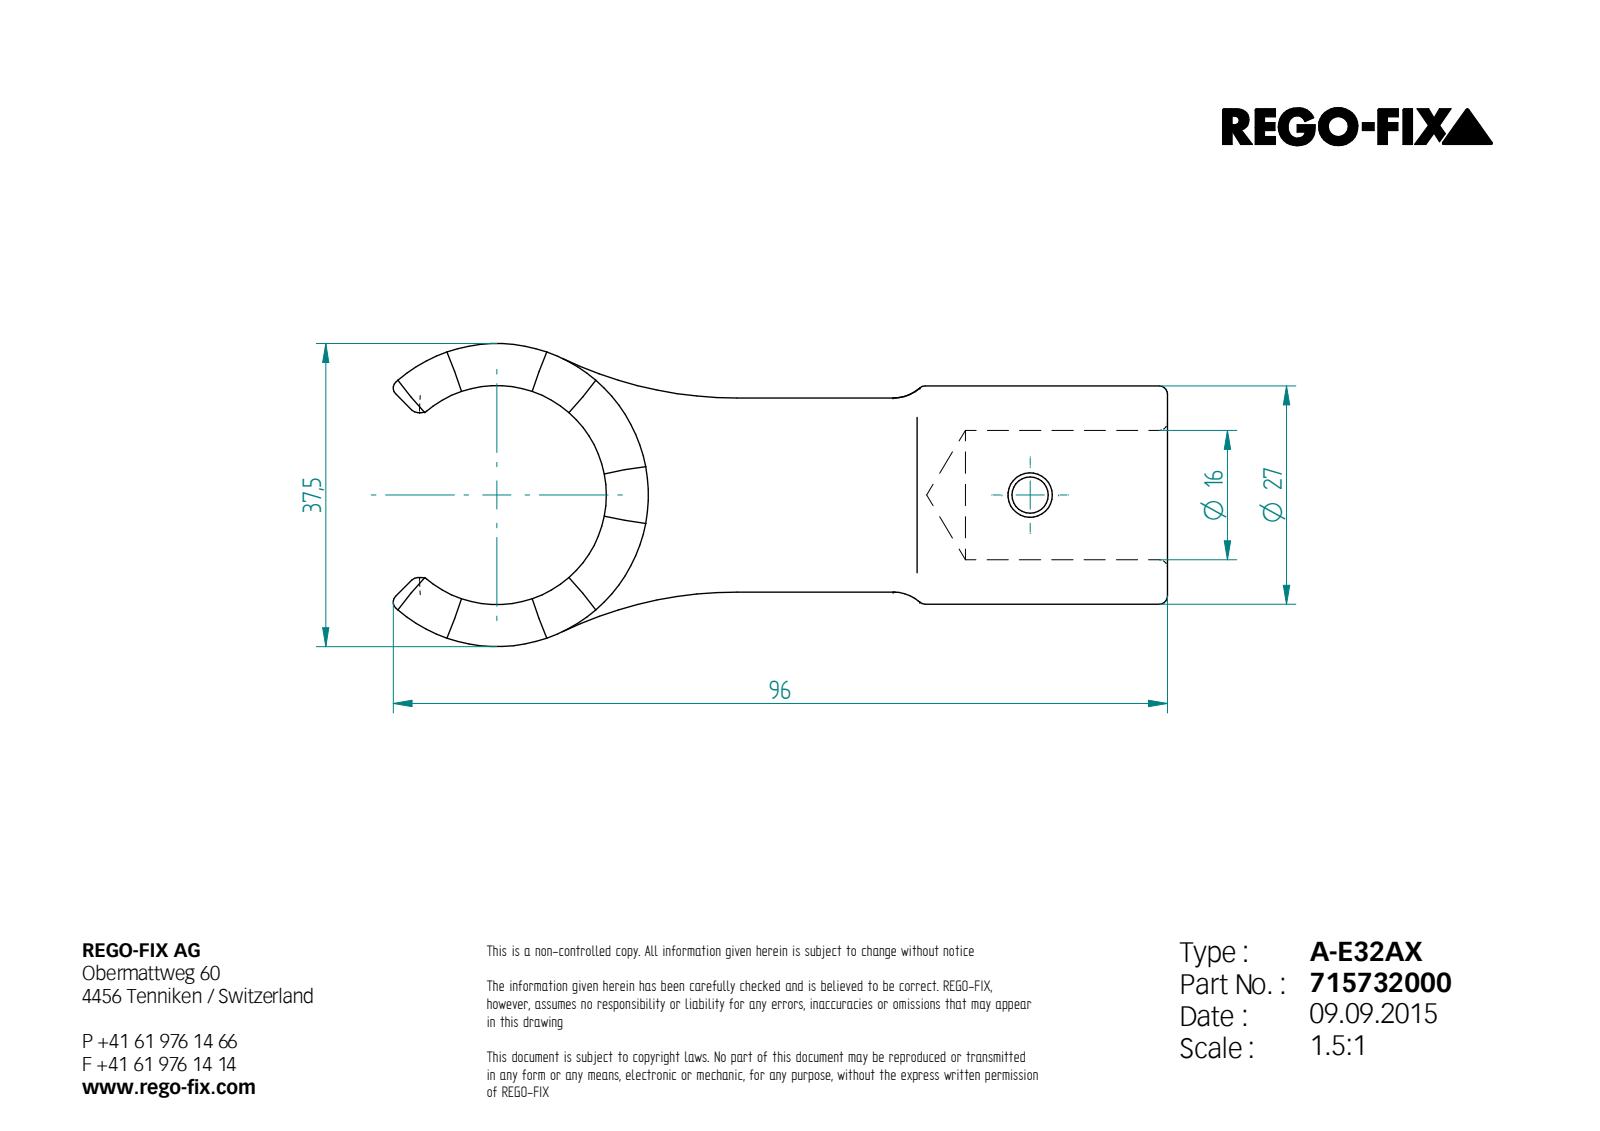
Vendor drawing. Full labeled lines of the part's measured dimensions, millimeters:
STEP written by: Unknown (AUTOMOTIVE_DESIGN)
Units: millimetres
Bodies: 1 solid, 88 faces (24 planar, 33 cylindrical, 31 other)
Overall size (bounding box): 95.82 × 37.5 × 27
Volume: 22 378 mm³ · Surface area: 9 525 mm²
Round holes (diameter × count): ⌀4.5 ×1, ⌀5.5 ×1, ⌀16 ×1
Round bosses / shafts (diameter × count): ⌀27 ×1
Partial cylindrical surfaces — rounded edges, fillets, slot ends (radius × count): R44.45 ×8, R1 ×6, R2 ×6, R5 ×2, R50 ×2, R13.55 ×1, R18.75 ×1
Main face-to-face distances: 6, 12, 14, 8, 2, 31, 24, 1.8, 22.2, 20.4
